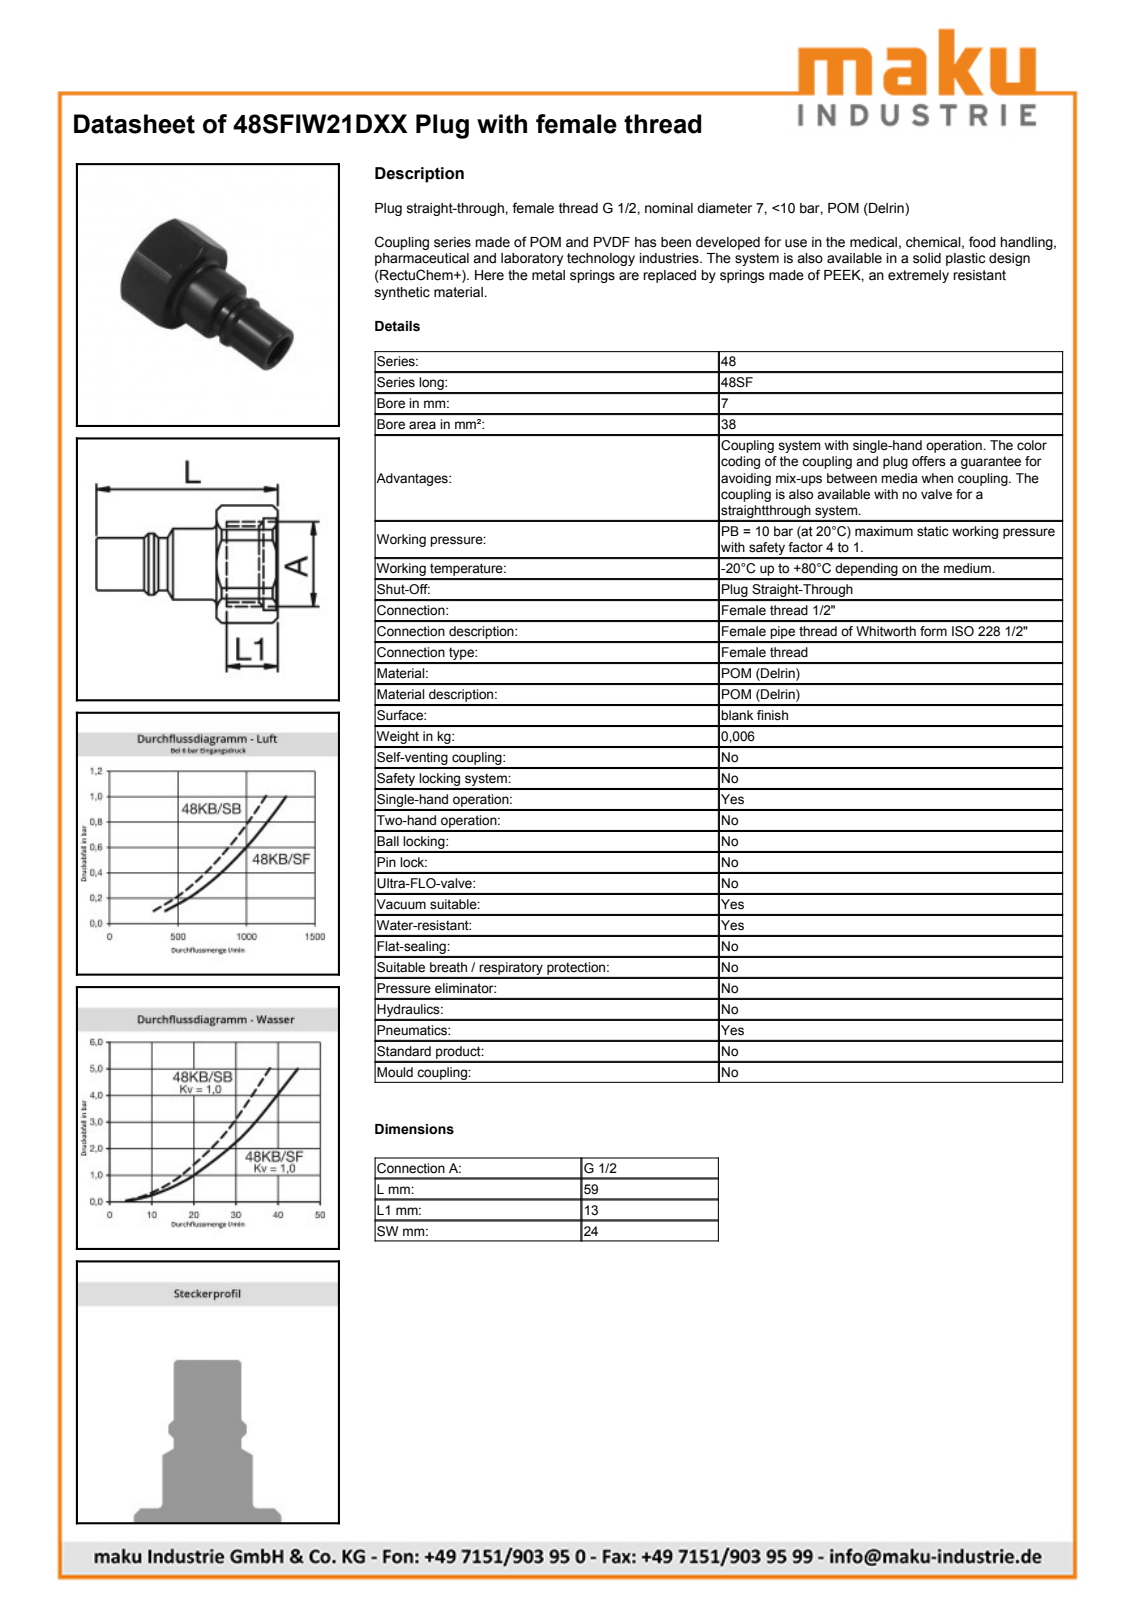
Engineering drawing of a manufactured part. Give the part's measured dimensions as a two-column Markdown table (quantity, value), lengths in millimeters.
| quantity | value |
| --- | --- |
| part name | D106298 |
| STEP written by | Autodesk Inventor 2011 (AUTOMOTIVE_DESIGN) |
| units | millimeters |
| bodies | 1 solid, 43 faces (10 planar, 13 cylindrical, 20 other) |
| overall size | 38.5 × 26.4 × 24 |
| volume | 5 033 mm³ |
| surface area | 4 284 mm² |
| round holes (diameter × count) | 7 × 1, 10.2 × 1, 18.63 × 1 |
| round bosses / shafts (diameter × count) | 13.9 × 1, 12 × 1, 10.3 × 1 |
| partial cylindrical surfaces (radius × count) | 13.2 × 1 |
| main face-to-face distances | 24, 2, 15, 13, 23.5, 25.5, 38.5 |
